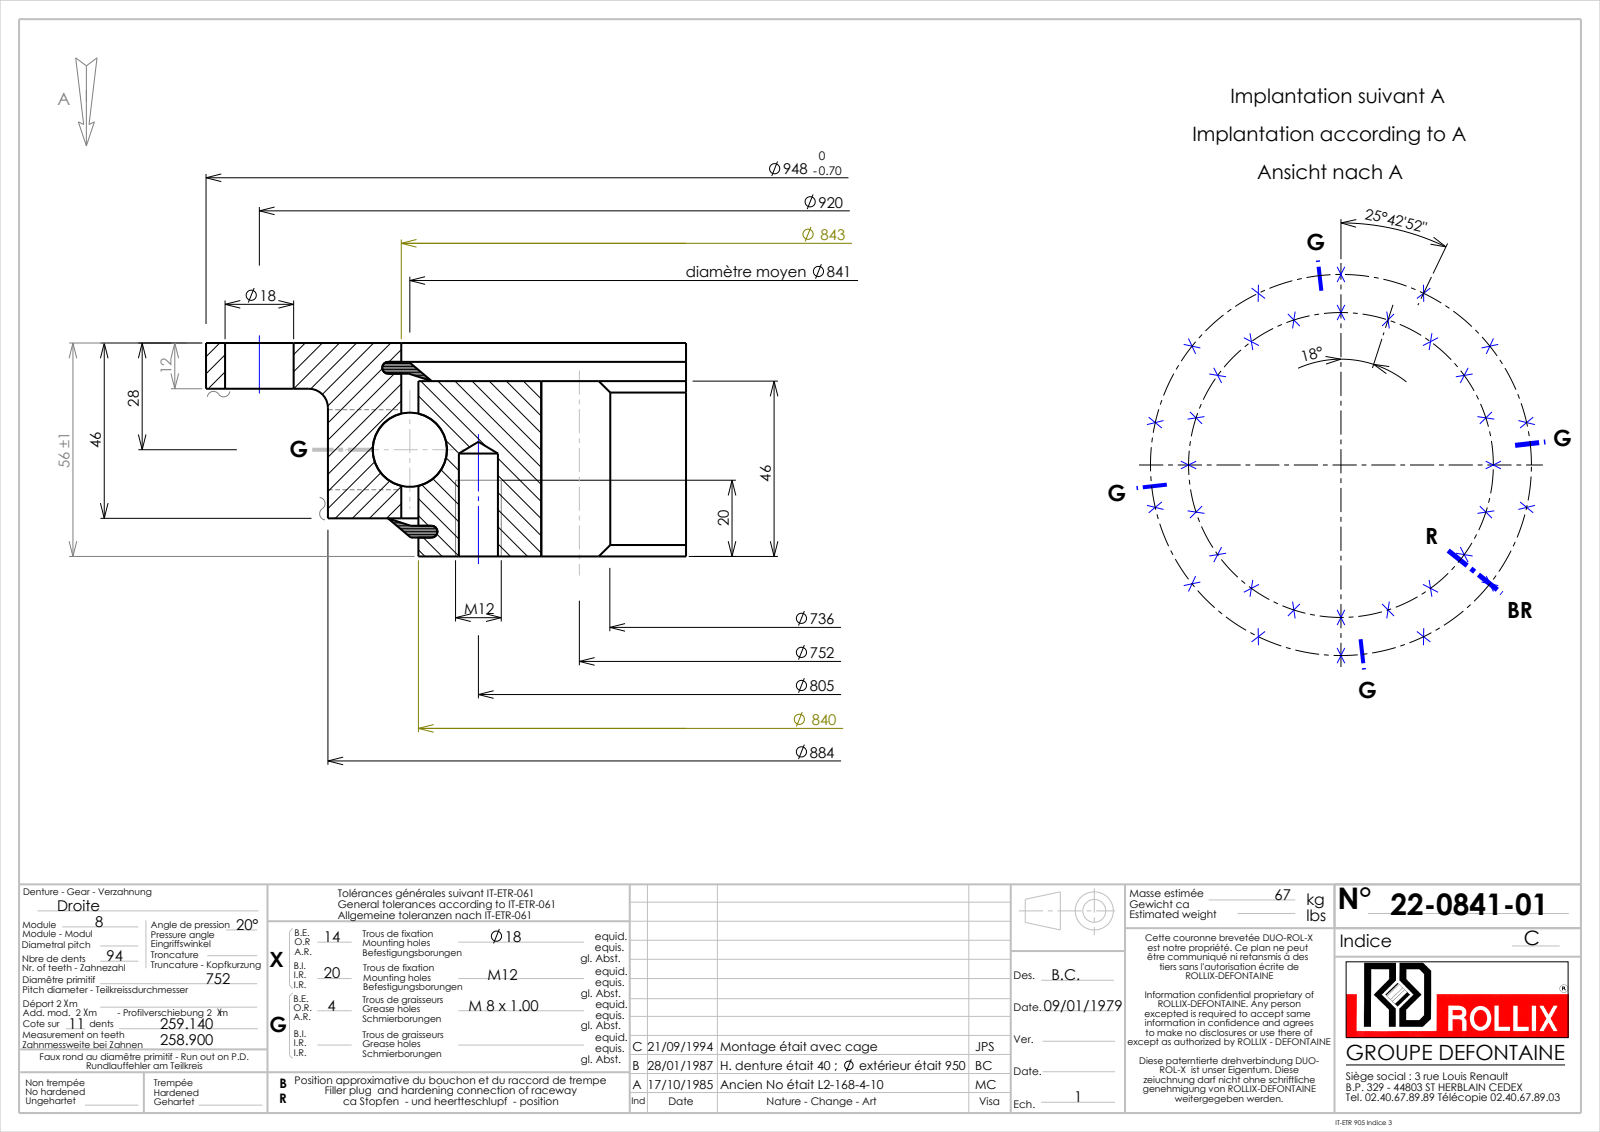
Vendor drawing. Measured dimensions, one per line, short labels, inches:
name: 22-0841-01
written by: SolidWorks 2016 (CONFIG_CONTROL_DESIGN)
unit: in
bodies: 9 solids, 828 faces (241 planar, 289 cylindrical, 298 other)
size: 37.323 × 37.323 × 2.205
volume: 472.7 in³; area: 2 080 in²
holes: 20× ⌀0.404, 14× ⌀0.709, 4× ⌀0.276, 1× ⌀33.287
bosses: 4× ⌀0.315, 1× ⌀37.323, 1× ⌀34.803, 1× ⌀32.933
rounds: 1× R14.488, 1× R15.197
face distances: 0.394, 1.811, 2.205, 1.732, 0.079, 0.472, 1.339, 1.417, 0.195, 2.01
hole spacings: 9.794, 14.388, 22.41, 25.64, 28.239, 30.142, 31.303, 4.958
